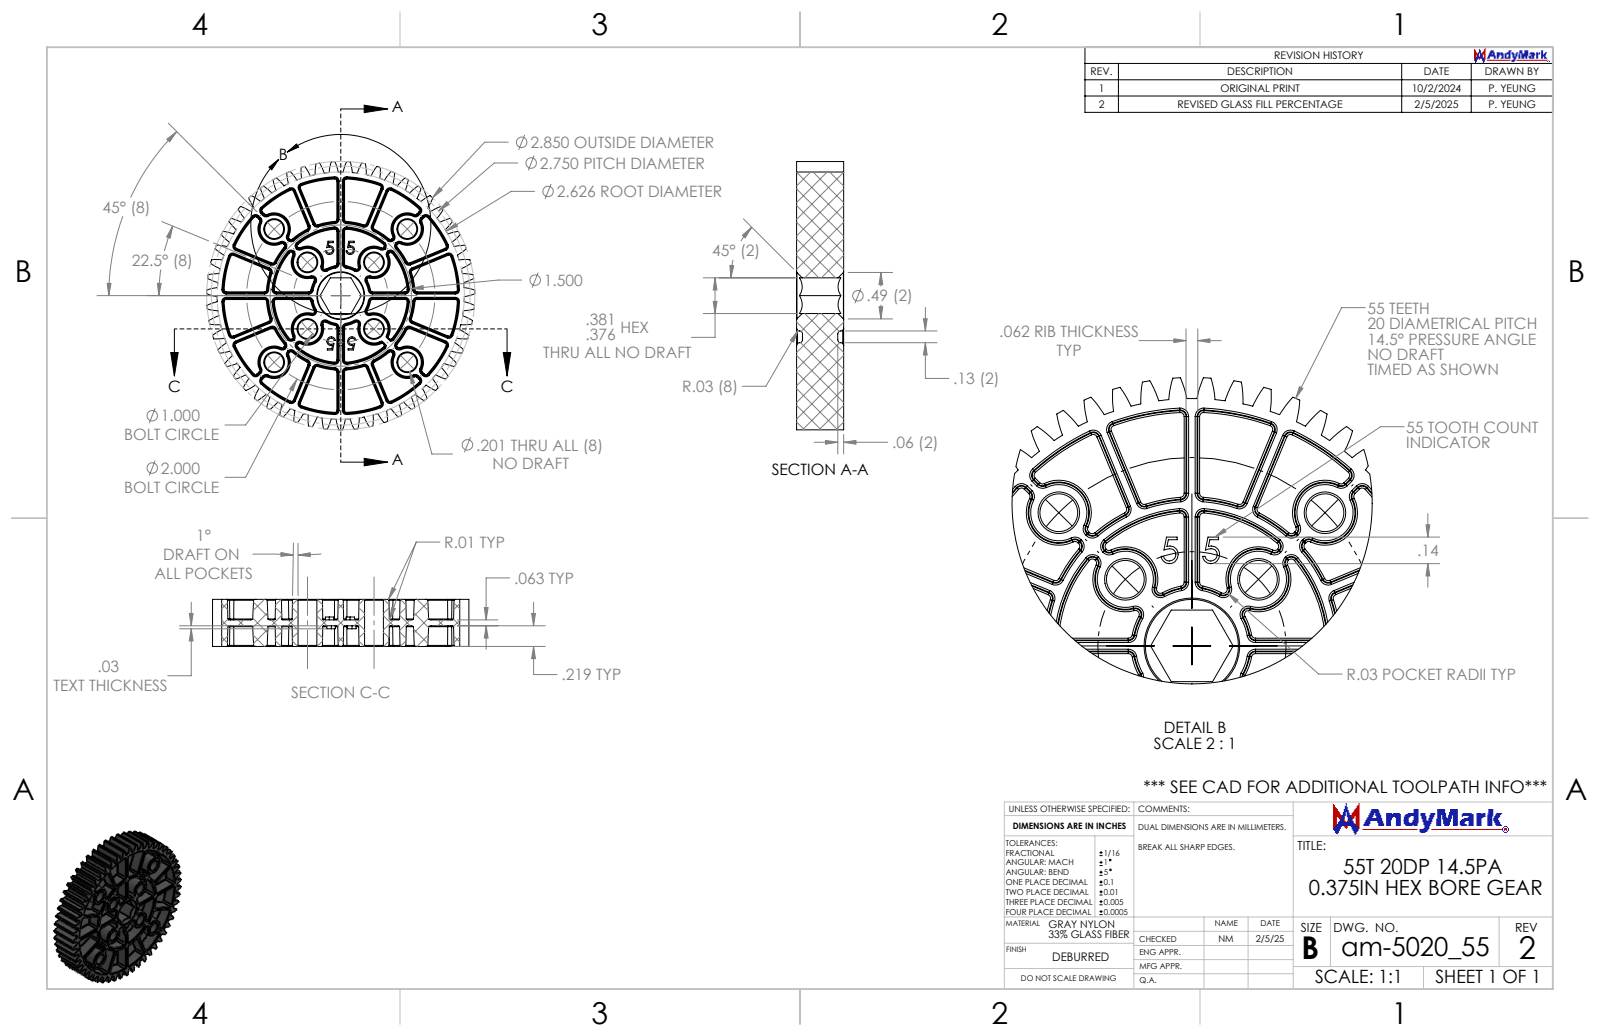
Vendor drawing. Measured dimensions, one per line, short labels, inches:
name: am-5020_55 55T 20DP 14.5PA 0.50 IN FW 0.375 Hex Gear
written by: SolidWorks 2024 (AUTOMOTIVE_DESIGN)
unit: in
bodies: 1 solid, 2144 faces (226 planar, 478 cylindrical, 1440 other)
size: 2.85 × 2.849 × 0.5
volume: 1.349 in³; area: 38.98 in²
holes: 8× ⌀0.201
rounds: 110× R0.55, 78× R0.01, 8× R0.031, 1× R1.313, 1× R1.425
face distances: 0.219, 0.281, 0.062, 0.064, 0.5, 0.38, 0.187, 0.313, 0.031, 0.094
hole spacings: 1.118, 0.5, 0.707, 1.414, 1.5, 1, 2
